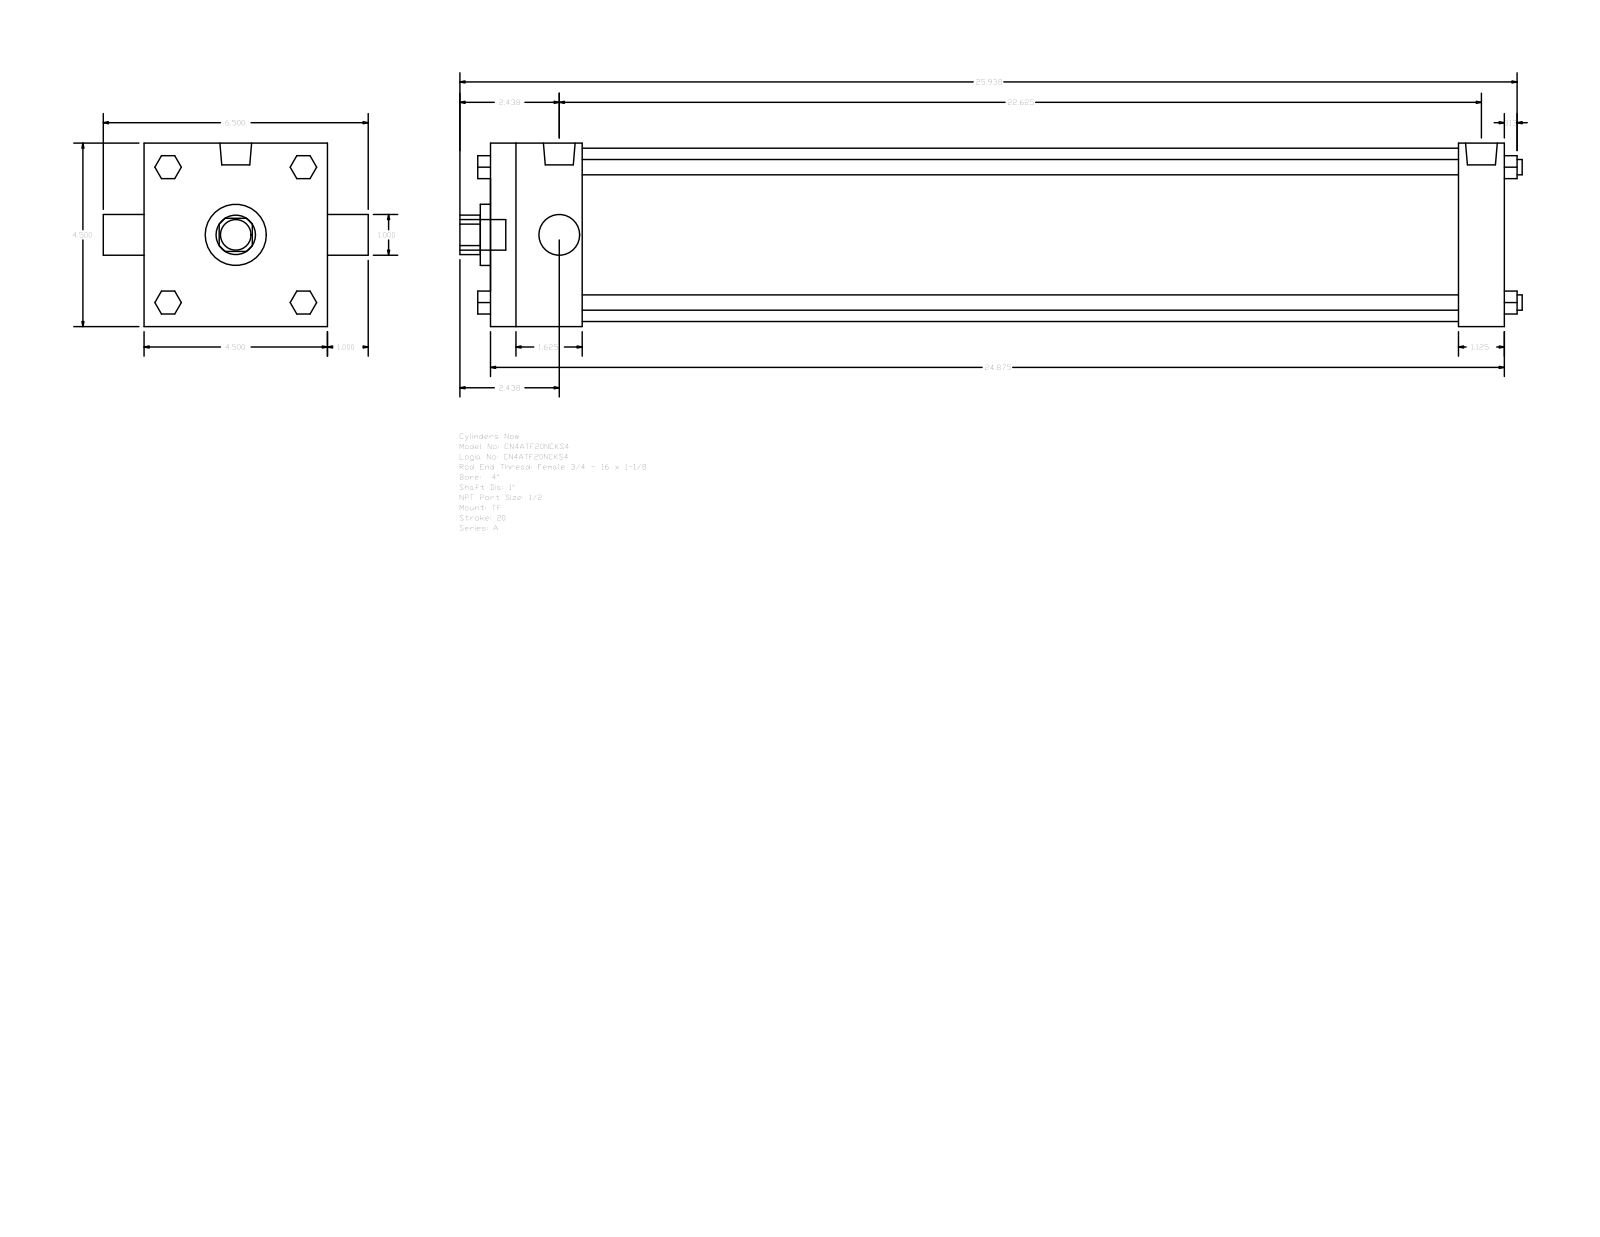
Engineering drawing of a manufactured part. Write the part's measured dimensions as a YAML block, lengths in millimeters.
part_name: "A_TF__0400_1"
step_written_by: "GSSL Pune (CONFIG_CONTROL_DESIGN)"
units: millimeters
bodies: {solids: 0, faces: 120, planar: 92, cylindrical: 28, other: 0}
overall_size: [661.99, 165.1, 114.3]
round_holes:
  - {diameter: 25.4, count: 2}
  - {diameter: 38.1, count: 1}
  - {diameter: 107.95, count: 1}
round_bosses_or_shafts:
  - {diameter: 9.53, count: 4}
  - {diameter: 8.73, count: 3}
  - {diameter: 19.77, count: 2}
  - {diameter: 19.05, count: 1}
partial_cylinders:
  - {radius: 12.29, count: 1}
face_to_face_distances: [114.3, 631.83, 603.25, 28.58, 57.15, 546.1, 574.68, 14.29, 42.16, 73.03]
